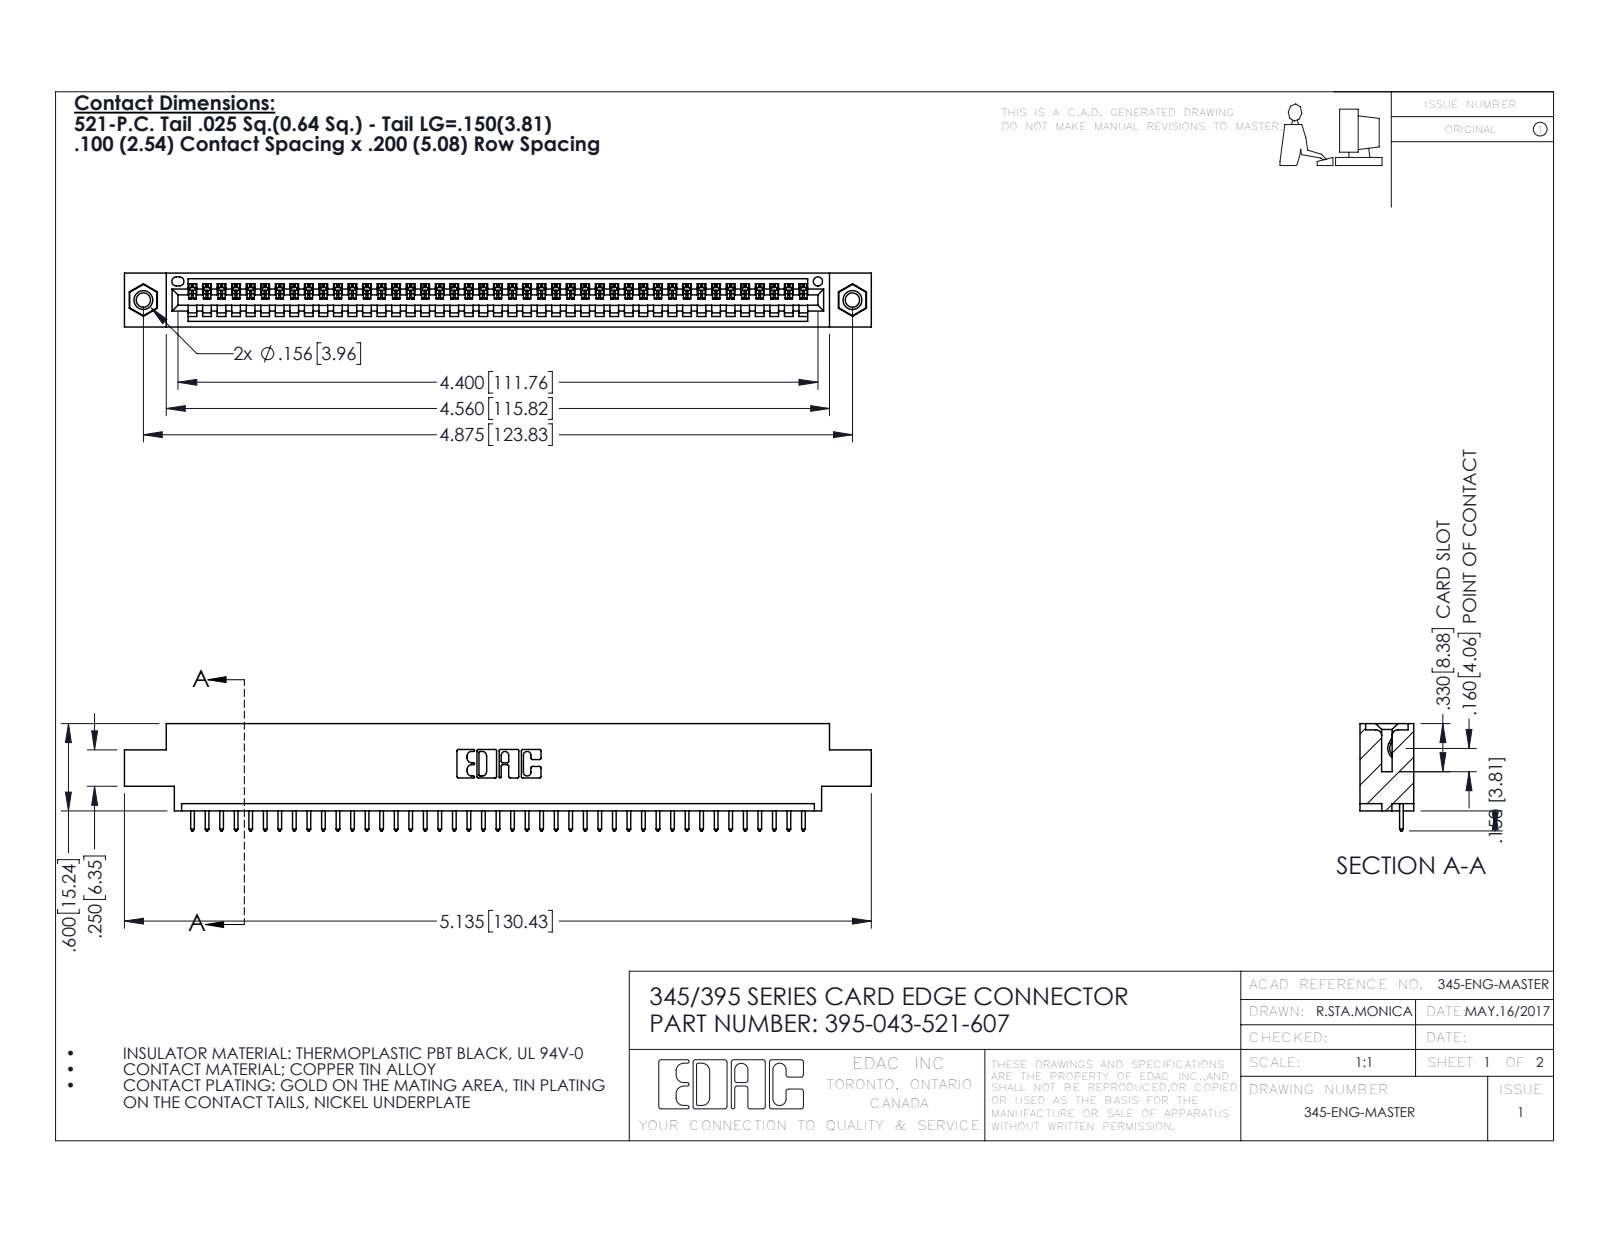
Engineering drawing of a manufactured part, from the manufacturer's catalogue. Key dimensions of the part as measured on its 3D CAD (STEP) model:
Part name (STEP PRODUCT): 345 Part_0.170 Offset - 0.156 Dia-TI; 345-292-001_345-293-121; 395-043-521-607; 345-250-001_345-250-005-103
STEP written by: SolidWorks 2016 (CONFIG_CONTROL_DESIGN)
Units: inches
Bodies: 46 solids, 2684 faces (1836 planar, 832 cylindrical, 16 other)
Overall size (bounding box): 5.135 × 0.737 × 0.37
Volume: 0.741 in³ · Surface area: 24.55 in²
Round holes (diameter × count): ⌀0.098 ×2, ⌀0.125 ×2, ⌀0.156 ×2, ⌀0.064 ×1
Round bosses / shafts (diameter × count): ⌀0.155 ×2
Partial cylindrical surfaces — rounded edges, fillets, slot ends (radius × count): R0.006 ×86, R0.01 ×86, R0.01 ×22, R0.007 ×6, R0.031 ×6, R0.026 ×3, R0.031 ×2, R0.04 ×2
Main face-to-face distances: 0.072, 0.298, 0.37, 0.2, 0.098, 0.272, 0.025, 0.225, 0.175, 0.149
Hole centre spacings: 0.27, 4.639, 4.875
